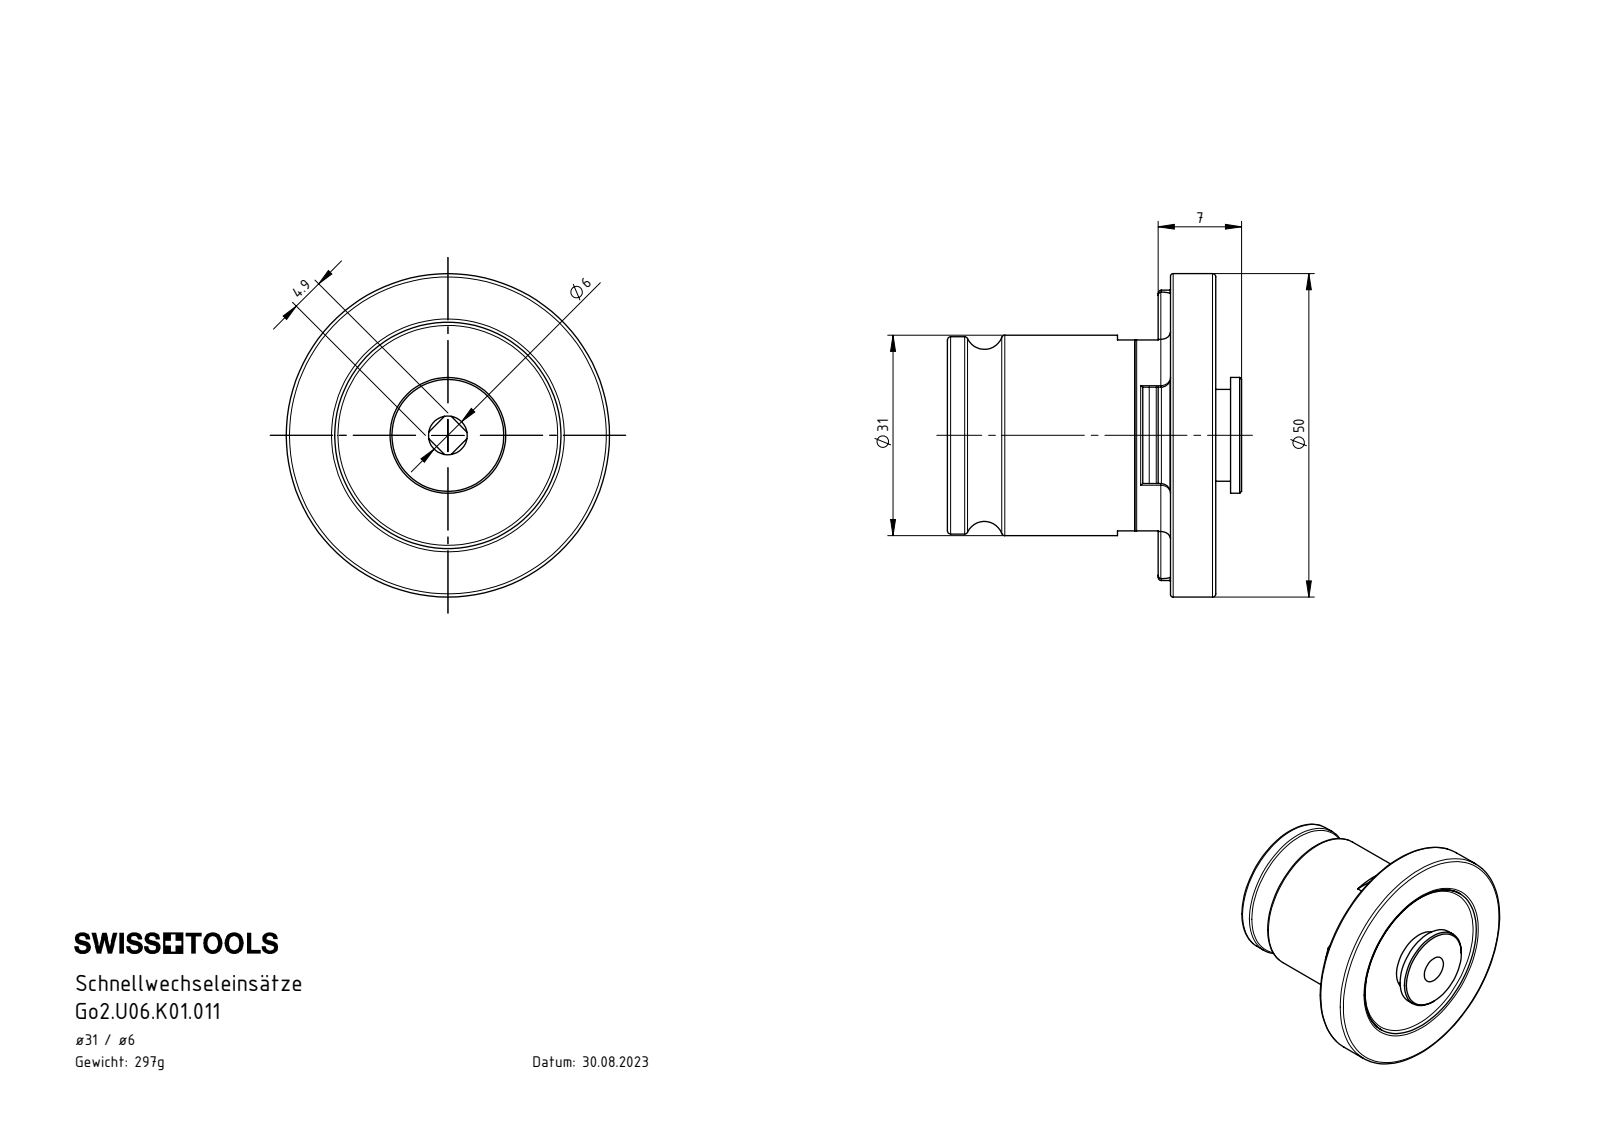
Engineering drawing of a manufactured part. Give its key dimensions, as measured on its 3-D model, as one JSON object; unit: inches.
{"part_name": "Go2.U06.K01.011", "step_written_by": "SolidWorks 2017 (AUTOMOTIVE_DESIGN)", "units": "inches", "bodies": {"solids": 1, "faces": 133, "planar": 37, "cylindrical": 39, "other": 57}, "overall_size": [1.969, 1.969, 1.791], "volume_in3": 2.31, "surface_area_in2": 15.33, "round_holes": [[0.236, 1], [0.791, 1]], "round_bosses_or_shafts": [[1.969, 1], [1.378, 1], [1.22, 1], [1.205, 1], [1.201, 1], [0.705, 1], [0.559, 1]], "partial_cylinders_radius": [[0.059, 5], [0.02, 4], [0.787, 1], [0.884, 1]], "face_to_face_distances": [0.026, 0.25, 0.276, 1.358, 1.608, 1.634, 0.118, 1.24, 1.49, 1.516]}
